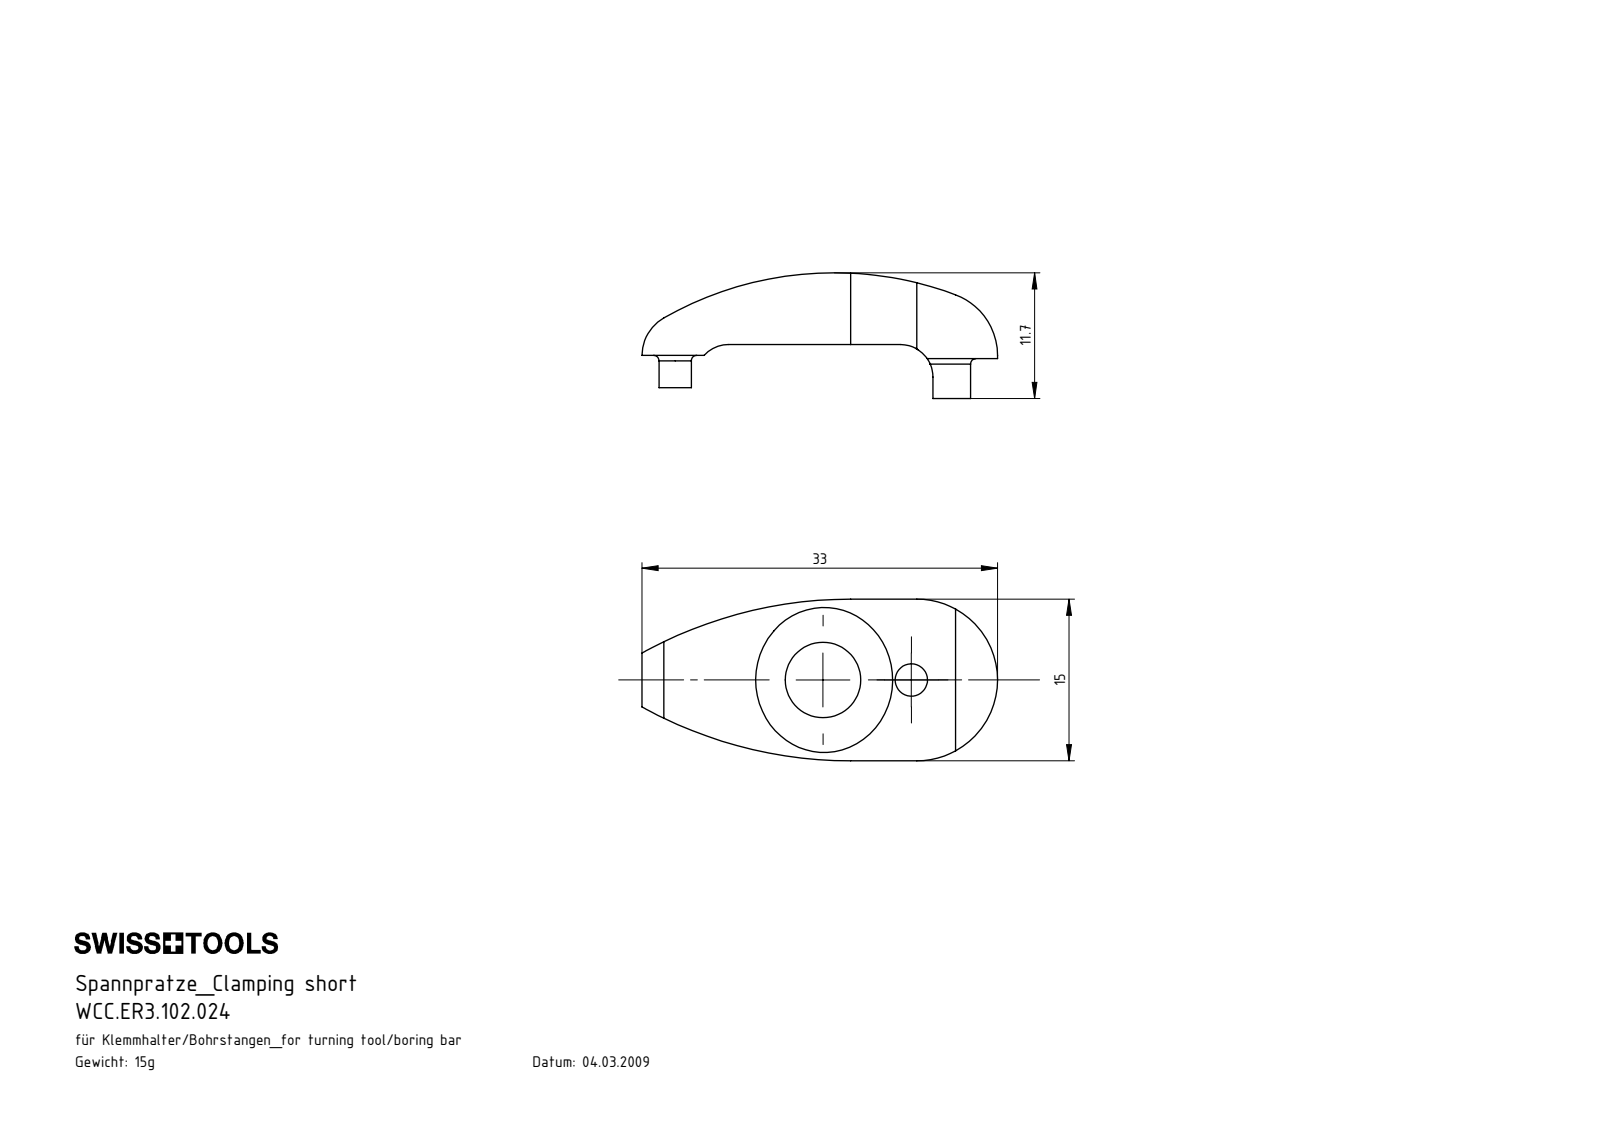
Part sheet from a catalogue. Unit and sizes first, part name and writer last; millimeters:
Units: millimetres
Overall size (bounding box): 33 × 16.6 × 15
Round holes (diameter × count): ⌀3 ×1, ⌀7 ×1
Round bosses / shafts (diameter × count): ⌀4 ×1, ⌀3 ×1
Partial cylindrical surfaces — rounded edges, fillets, slot ends (radius × count): R3 ×2, R40 ×2, R4 ×1, R6 ×1, R7.5 ×1, R32 ×1
Main face-to-face distances: 1.3, 1, 15, 4, 3.7, 5, 2.7, 3, 16.6, 15.6
Hole centre spacings: 8.2
Volume: 1 990 mm³ · Surface area: 1 537 mm²
Bodies: 2 solids, 46 faces (15 planar, 20 cylindrical, 11 other)
Part name (STEP PRODUCT): WCC-ER3.102.024_C; WCC.ER3.102.024; ISO 8745-3x12
STEP written by: SolidWorks 2017 (AUTOMOTIVE_DESIGN)
